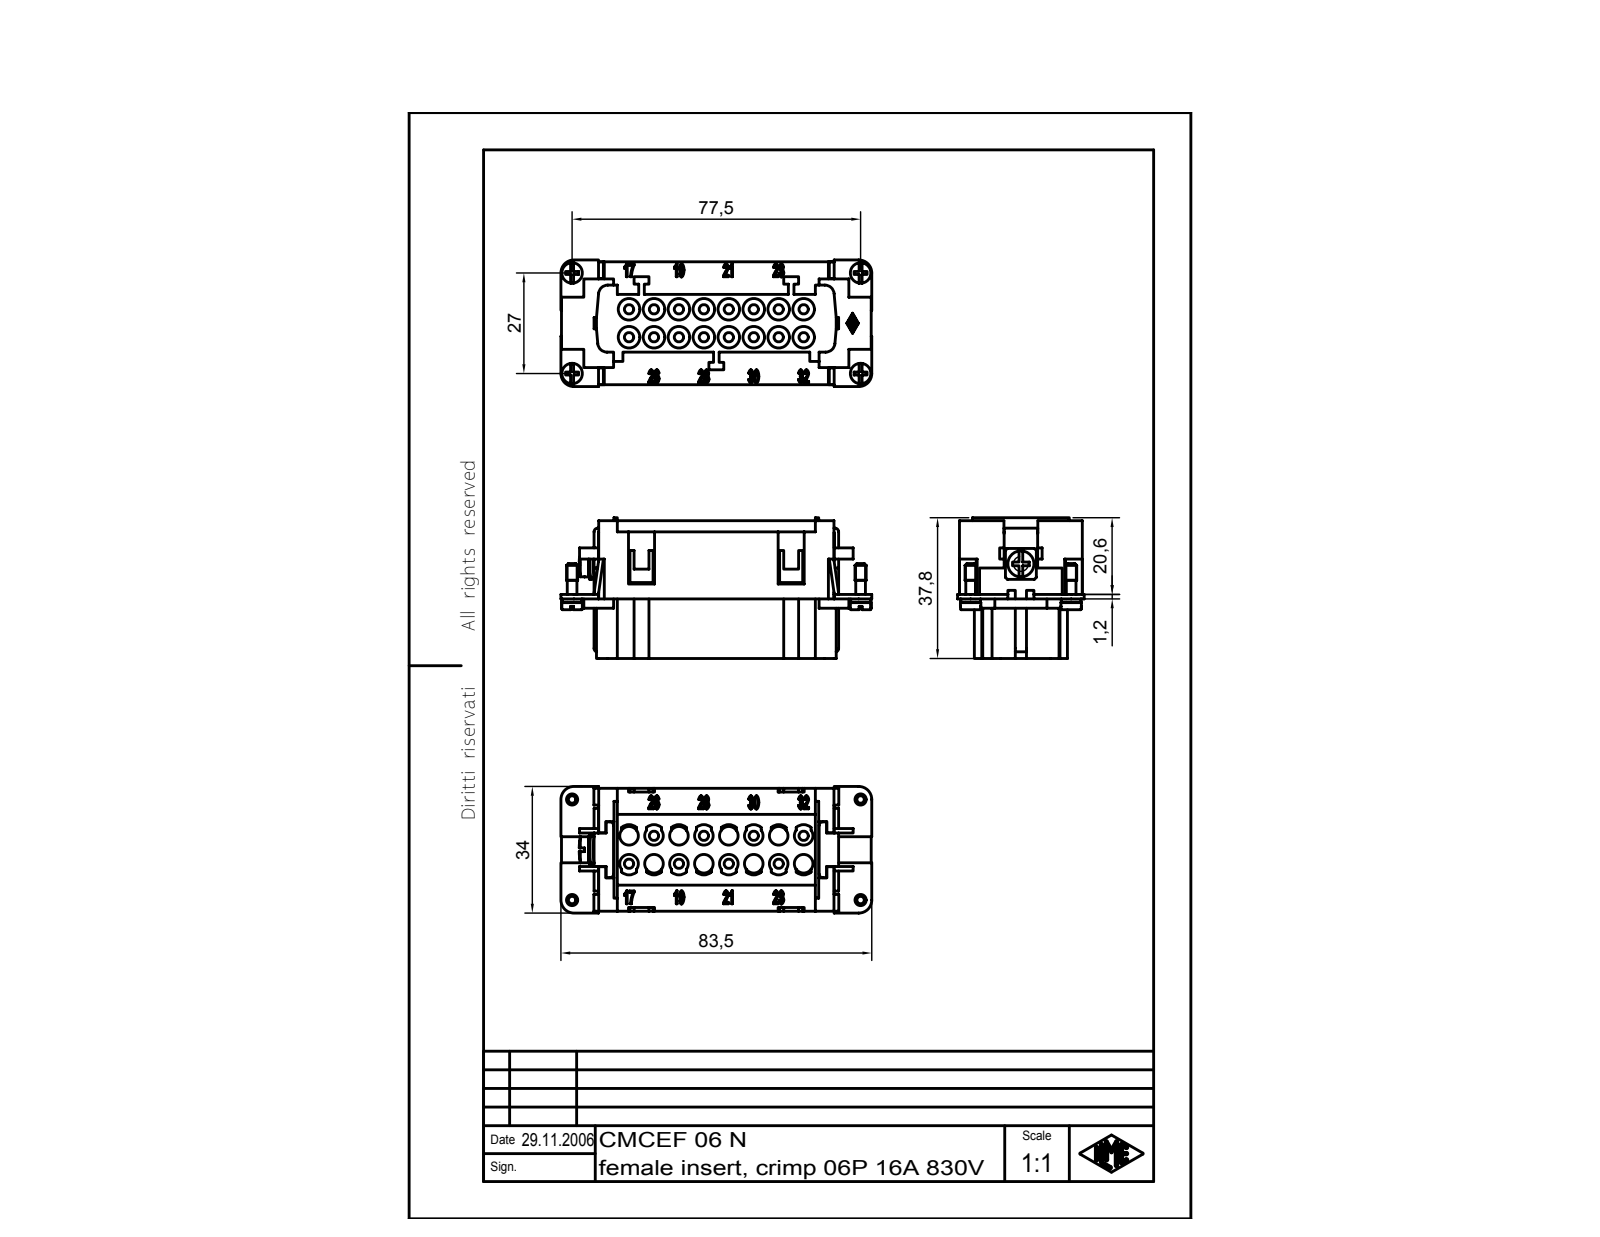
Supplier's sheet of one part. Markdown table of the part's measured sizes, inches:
| quantity | value |
| --- | --- |
| part name | CMCEF 06 N |
| STEP written by | Autodesk Inventor 7 (AUTOMOTIVE_DESIGN) |
| units | inches |
| bodies | 2 solids, 1175 faces (451 planar, 94 cylindrical, 630 other) |
| overall size | 3.287 × 1.488 × 1.339 |
| volume | 3.315 in³ |
| surface area | 36.73 in² |
| round holes (diameter × count) | 0.197 × 4, 0.128 × 1 |
| round bosses / shafts (diameter × count) | 0.217 × 2, 0.209 × 2, 0.118 × 2, 0.102 × 2, 0.276 × 1 |
| partial cylindrical surfaces (radius × count) | 0.004 × 14, 0.098 × 12, 0.118 × 8, 0.039 × 4, 0.138 × 2, 0.217 × 1 |
| main face-to-face distances | 0.955, 0.344, 0.118, 0.827, 1.299, 0.709, 0.61, 0.039, 0.63, 0.059 |
| hole center spacings | 0.528, 1.055, 1.583 |
